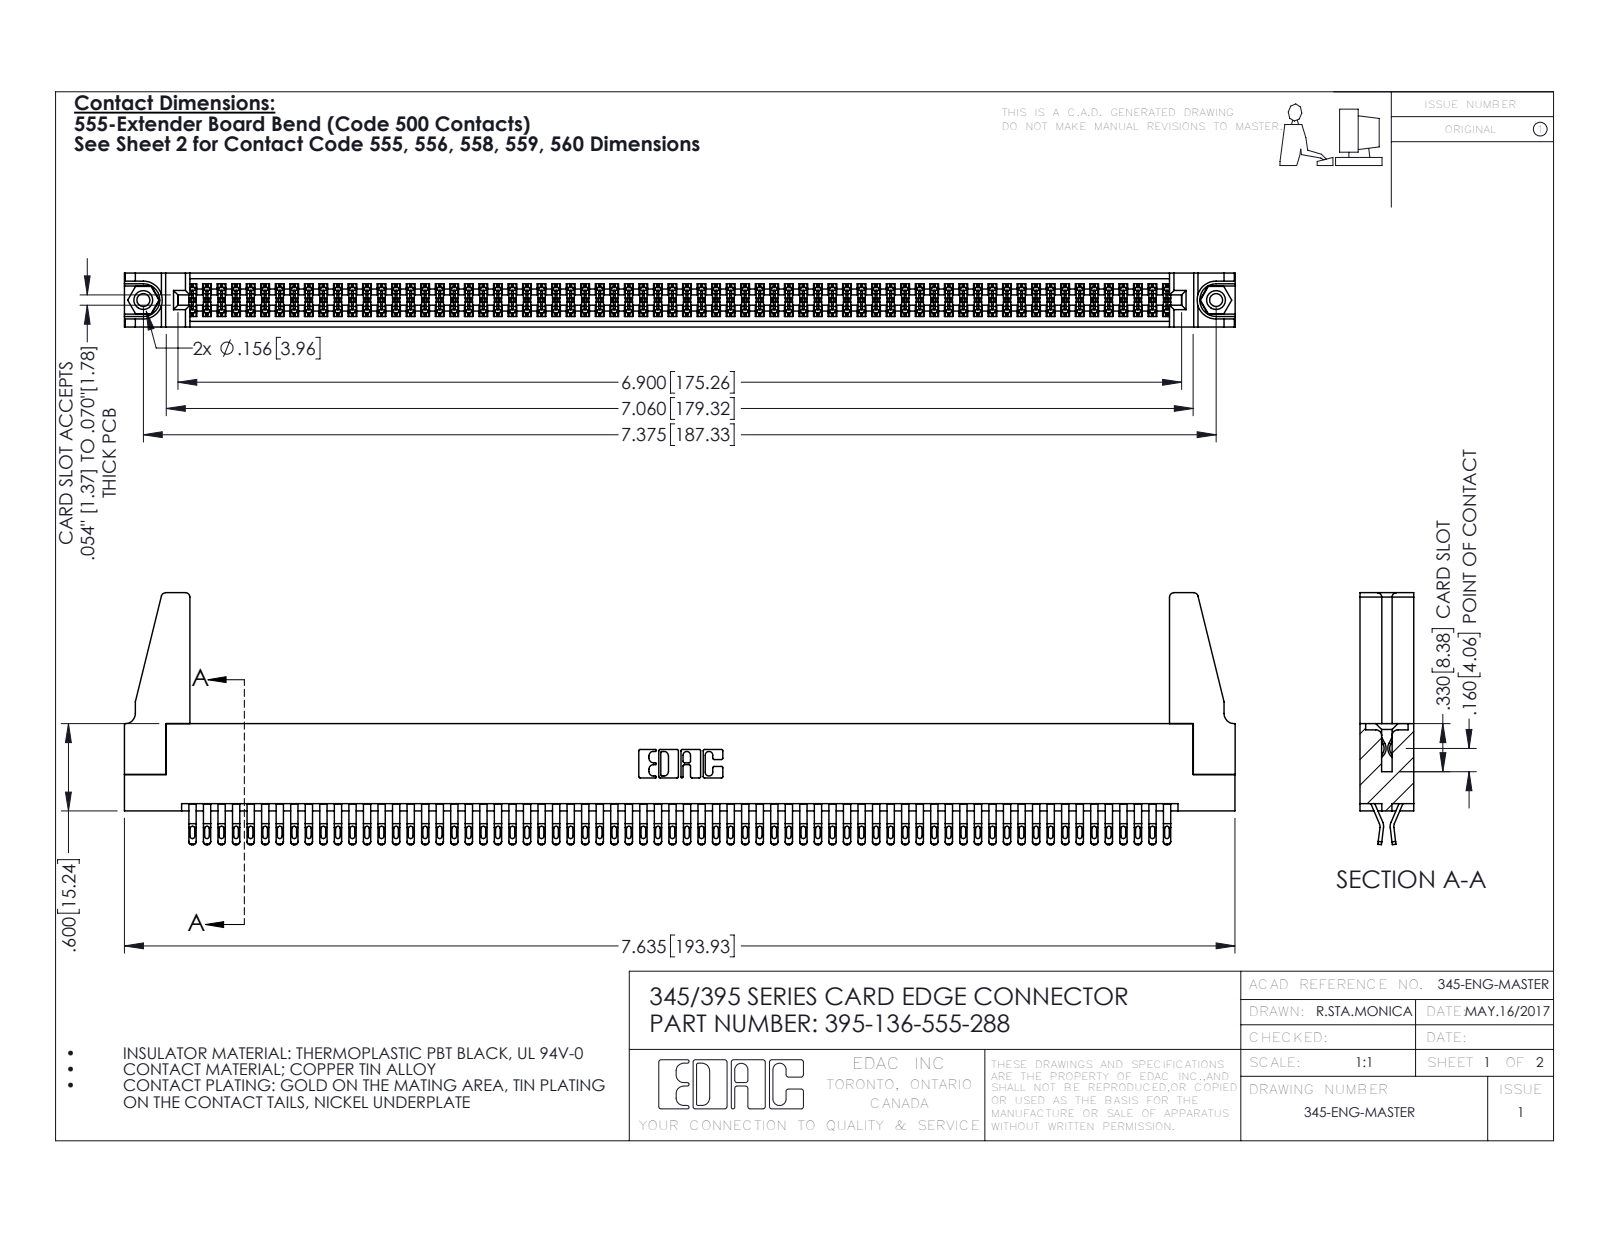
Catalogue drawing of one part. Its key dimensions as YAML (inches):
part_name: "345-220-078_345-220-088; 395-136-555-288; 345-292-001_555 Tail; 345-250-001_345-250-001-102 (+1 more)"
step_written_by: "SolidWorks 2016 (CONFIG_CONTROL_DESIGN)"
units: inches
bodies: {solids: 141, faces: 7866, planar: 4368, cylindrical: 3482, other: 16}
overall_size: [7.636, 1.732, 0.37]
volume: 1.387
surface_area: 52.37
round_holes:
  - {diameter: 0.089, count: 2}
  - {diameter: 0.125, count: 2}
  - {diameter: 0.156, count: 2}
  - {diameter: 0.064, count: 1}
round_bosses_or_shafts:
  - {diameter: 0.155, count: 2}
partial_cylinders:
  - {radius: 0.016, count: 340}
  - {radius: 0.02, count: 272}
  - {radius: 0.006, count: 204}
  - {radius: 0.01, count: 22}
  - {radius: 0.03, count: 8}
  - {radius: 0.007, count: 6}
  - {radius: 0.031, count: 6}
  - {radius: 0.026, count: 3}
face_to_face_distances: [0.072, 0.298, 0.37, 0.025, 0.2, 0.098, 0.272, 0.225, 0.175, 0.149]
hole_center_spacings: [0.27, 7.139, 7.375]
